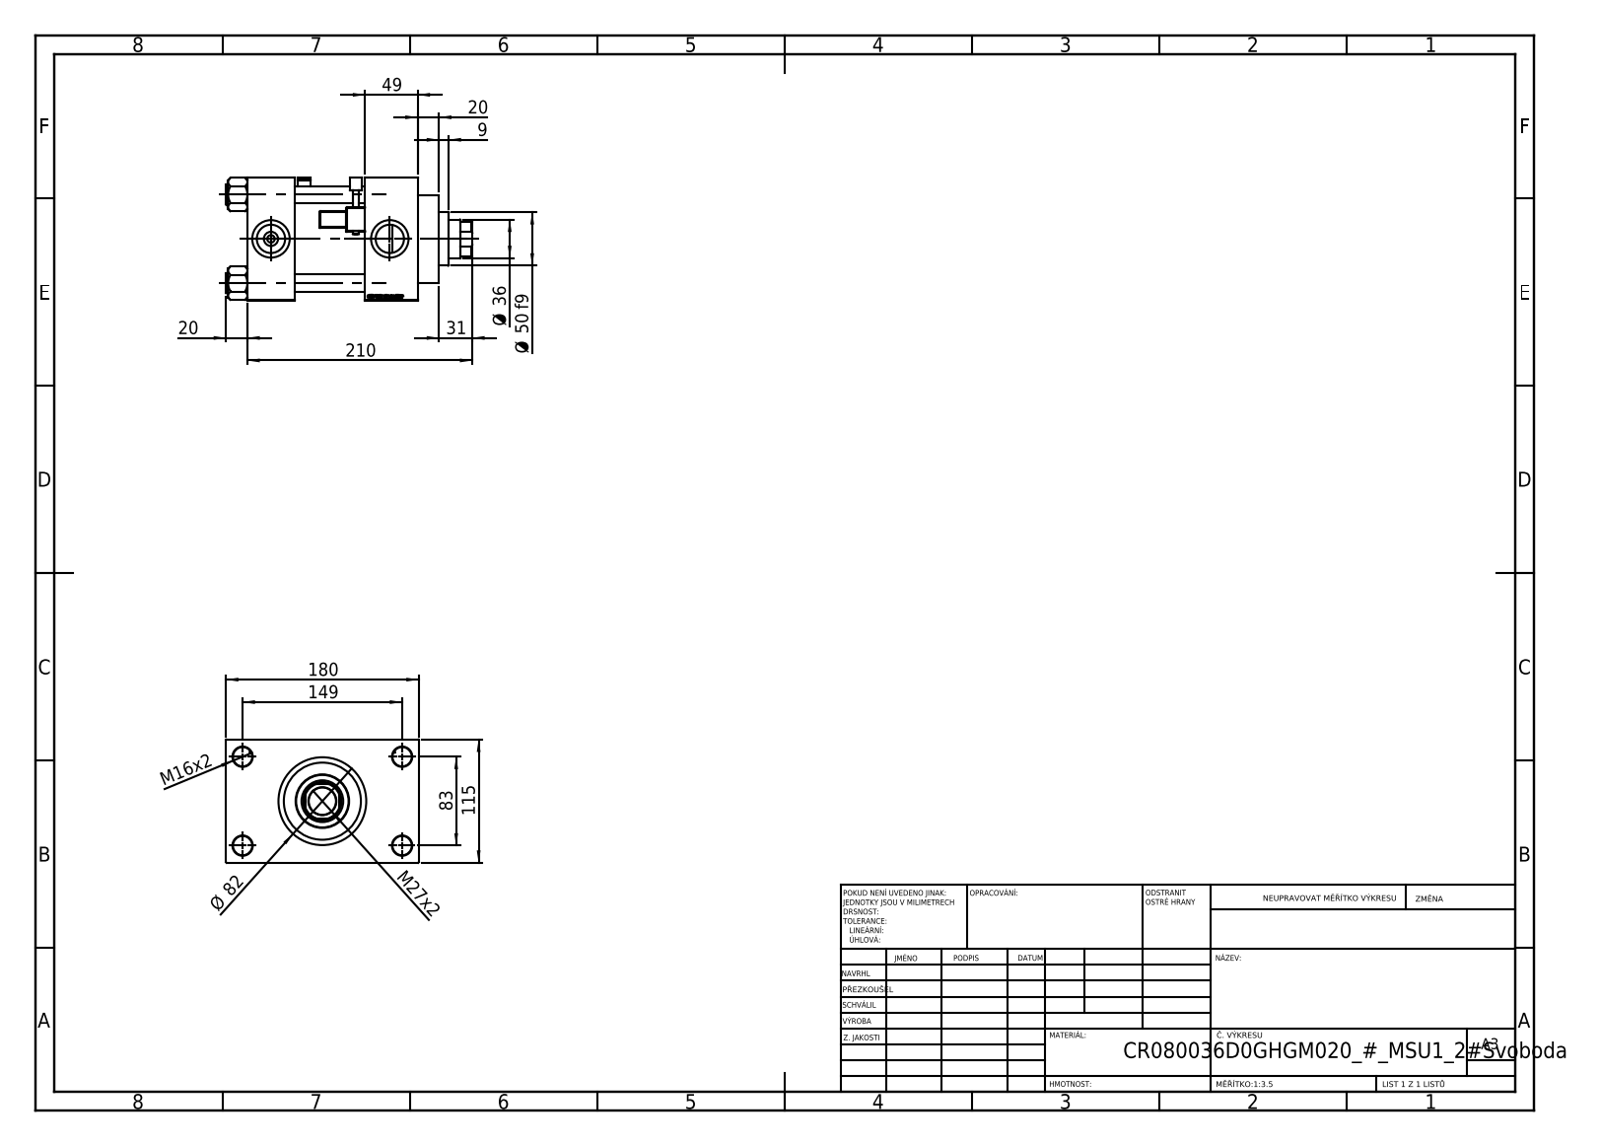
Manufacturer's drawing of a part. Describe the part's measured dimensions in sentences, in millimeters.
The part is named "V215_VC_A; V215CR_VCP_D; V215CR_D_TYCINKA; NUT_M5_D (+2 more)". Its 3-D file was written by "SolidWorks 2019 (CONFIG_CONTROL_DESIGN)". It is 13 solids with 1305 faces: 603 planar, 148 cylindrical and 554 other. Overall it measures 230 by 180 by 115 millimeters. Its volume is 2 021 000 cubic millimeters and its surface area 309 046 square millimeters. Round holes: 4 of diameter 16, 4 of diameter 18, 2 of diameter 7, 2 of diameter 26.44, 2 of diameter 35, 1 of diameter 25.5, 1 of diameter 36, 1 of diameter 39, 1 of diameter 61, 1 of diameter 72, 1 of diameter 80. Round bosses or shafts: 4 of diameter 19, 2 of diameter 6, 1 of diameter 86, 1 of diameter 82, 1 of diameter 50. Partial cylindrical surfaces (rounded edges, fillets, slot ends): 48 of radius 0.5, 2 of radius 1, 2 of radius 2.5, 2 of radius 4, 1 of radius 17.5. The main face-to-face distances are 115, 66, 110, 49, 44, 159, 32.5, 147.5, 20, 69. The hole center spacings are 33.15, 58.48, 82.7, 85.28, 89.24, 115.85, 142.43, 83.
